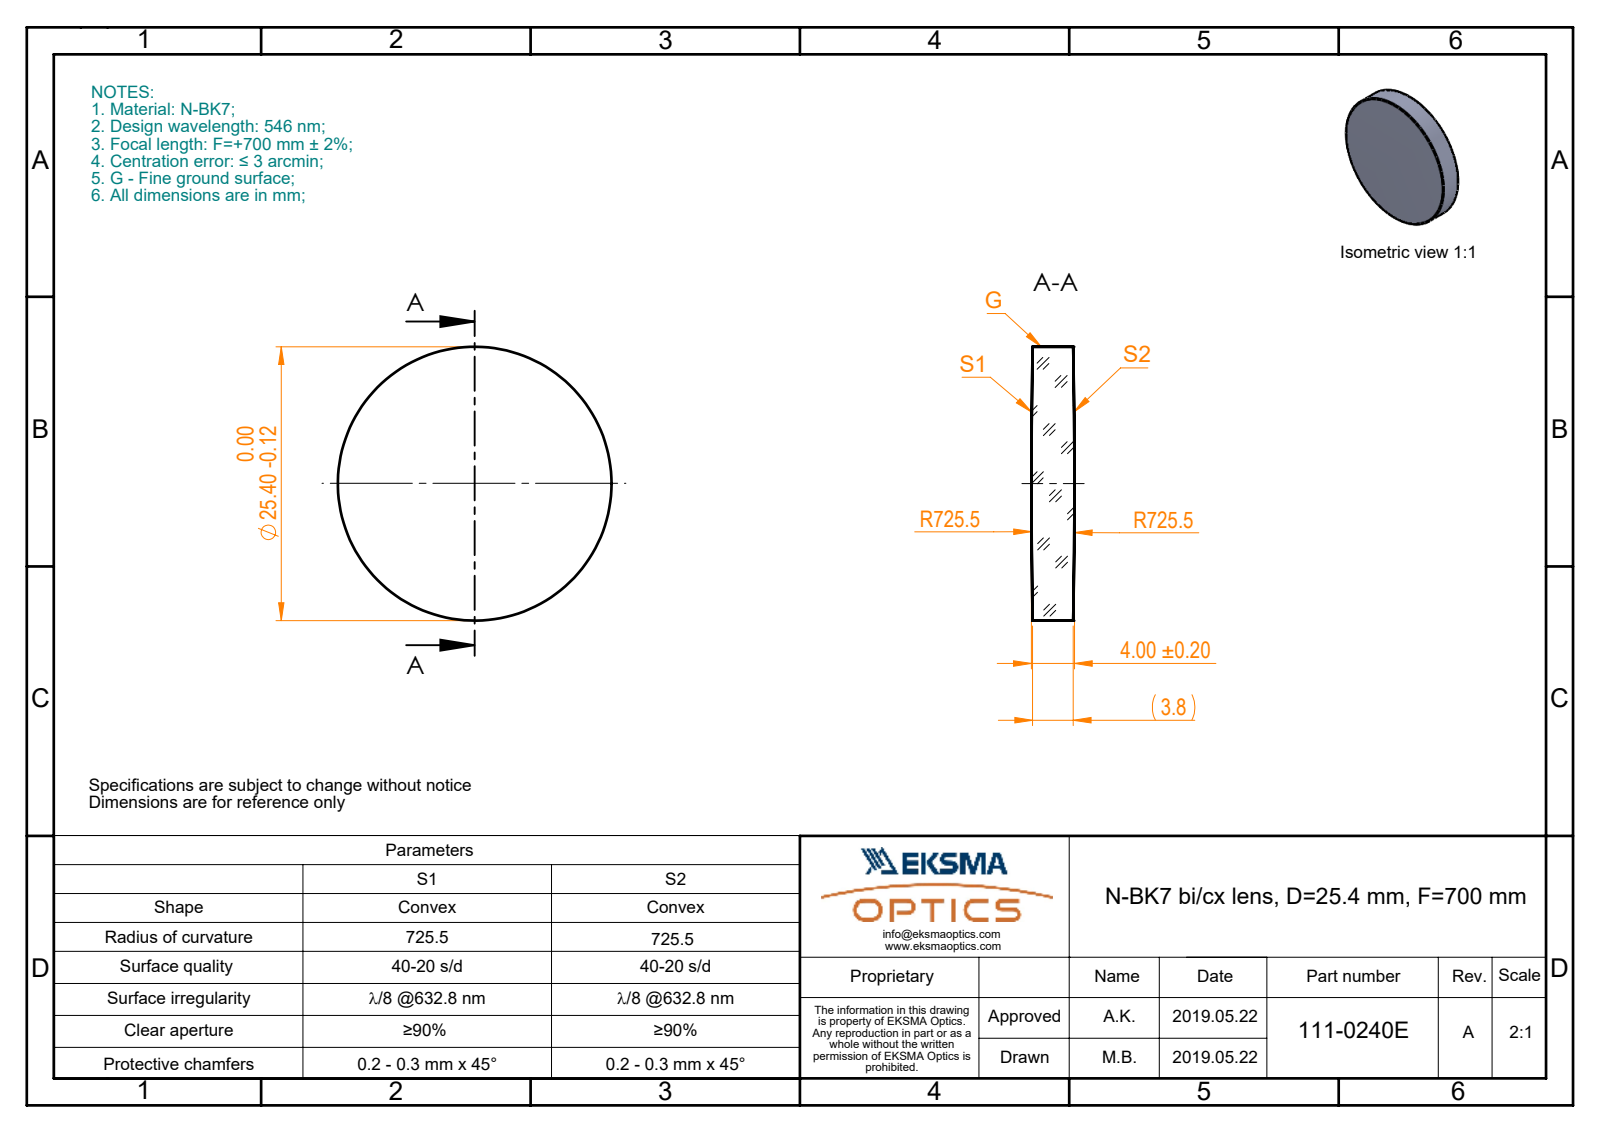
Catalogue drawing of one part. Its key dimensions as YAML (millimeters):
part_name: "111-0240E BK7 bi-cx 25.4 F700"
step_written_by: "SolidWorks 2017 (CONFIG_CONTROL_DESIGN)"
units: millimeters
bodies: {solids: 1, faces: 6, planar: 0, cylindrical: 2, other: 4}
overall_size: [25.4, 25.4, 4]
volume: 1971
surface_area: 1315
round_bosses_or_shafts:
  - {diameter: 25.4, count: 1}
